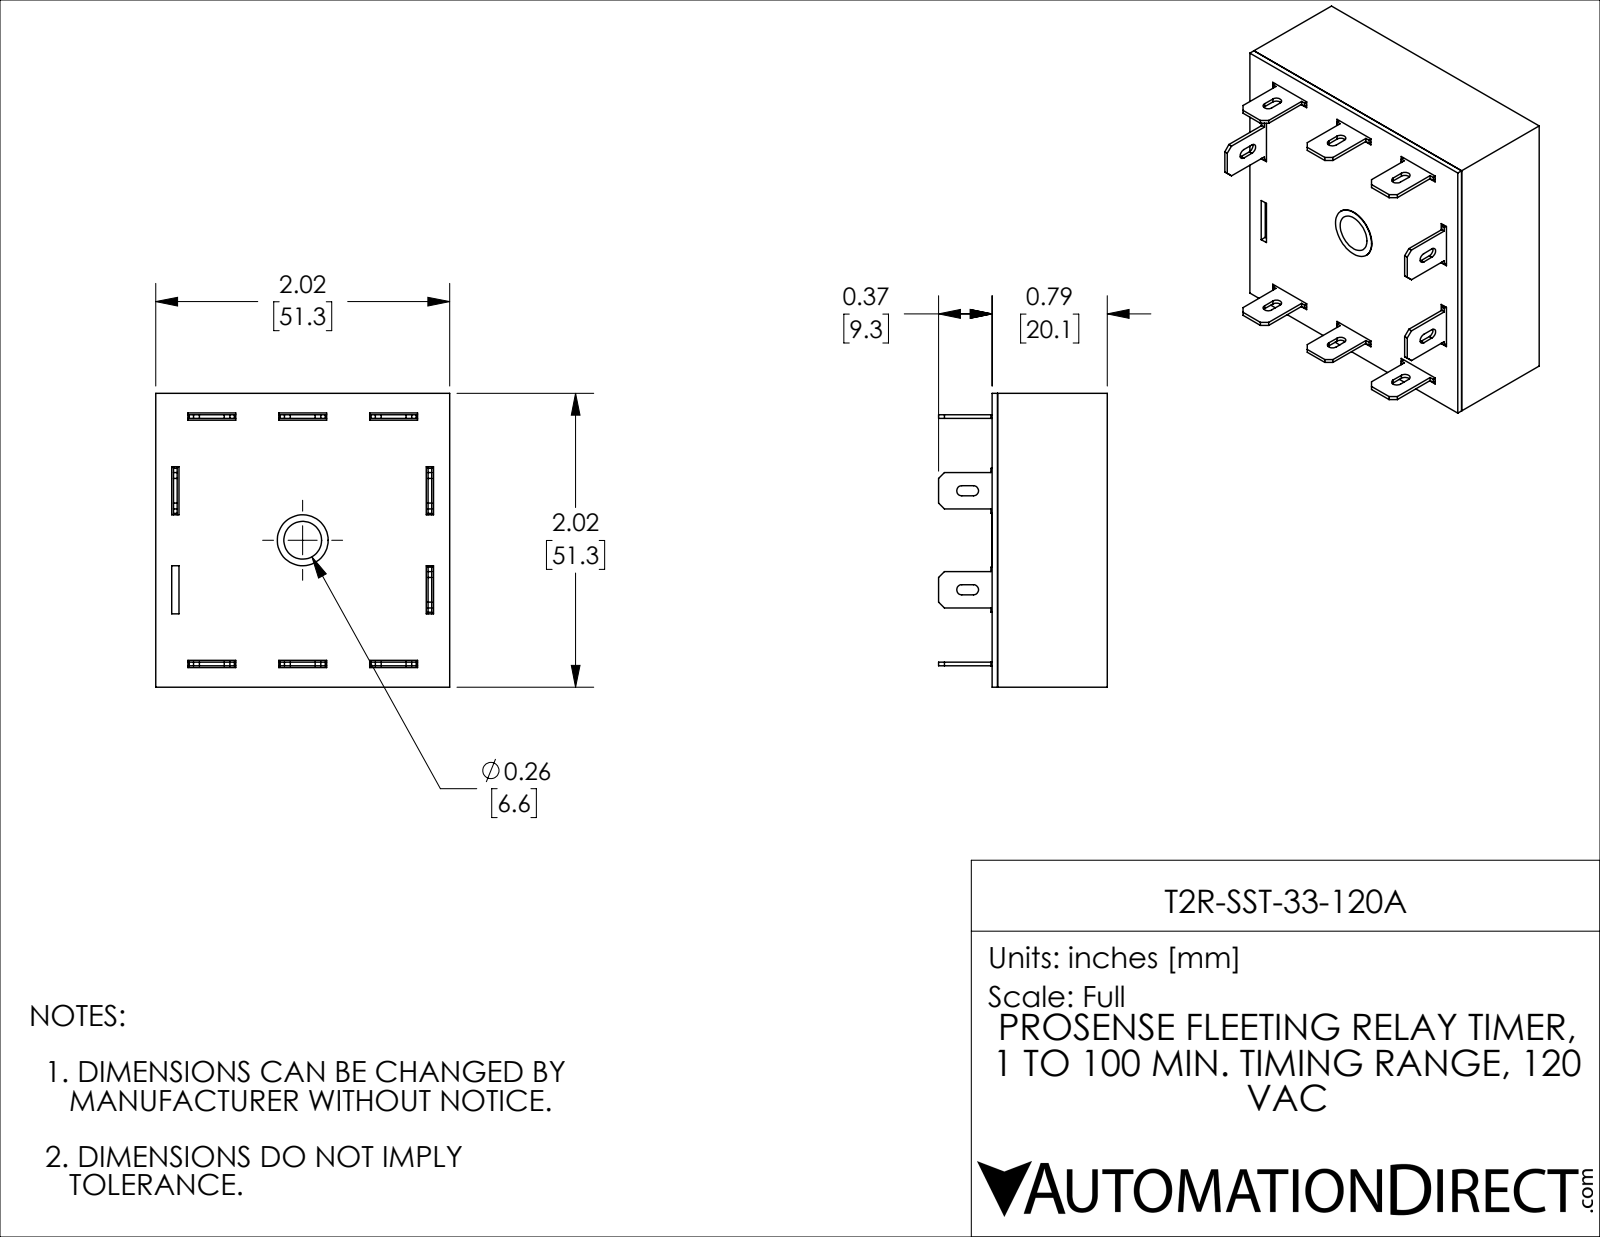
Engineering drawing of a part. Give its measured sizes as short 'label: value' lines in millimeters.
name: T2R-SST-33-120A
written by: SolidWorks 2021 (CONFIG_CONTROL_DESIGN)
unit: mm
bodies: 11 solids, 280 faces (256 planar, 22 cylindrical, 2 other)
size: 51.31 × 51.31 × 29.46
volume: 11 178 mm³; area: 23 301 mm²
holes: 1× ⌀8.89
rounds: 10× R0.89
face distances: 1.14, 50.16, 19.15, 20.12, 0.97, 18.01, 18.98, 51.3, 3.74, 47.56
